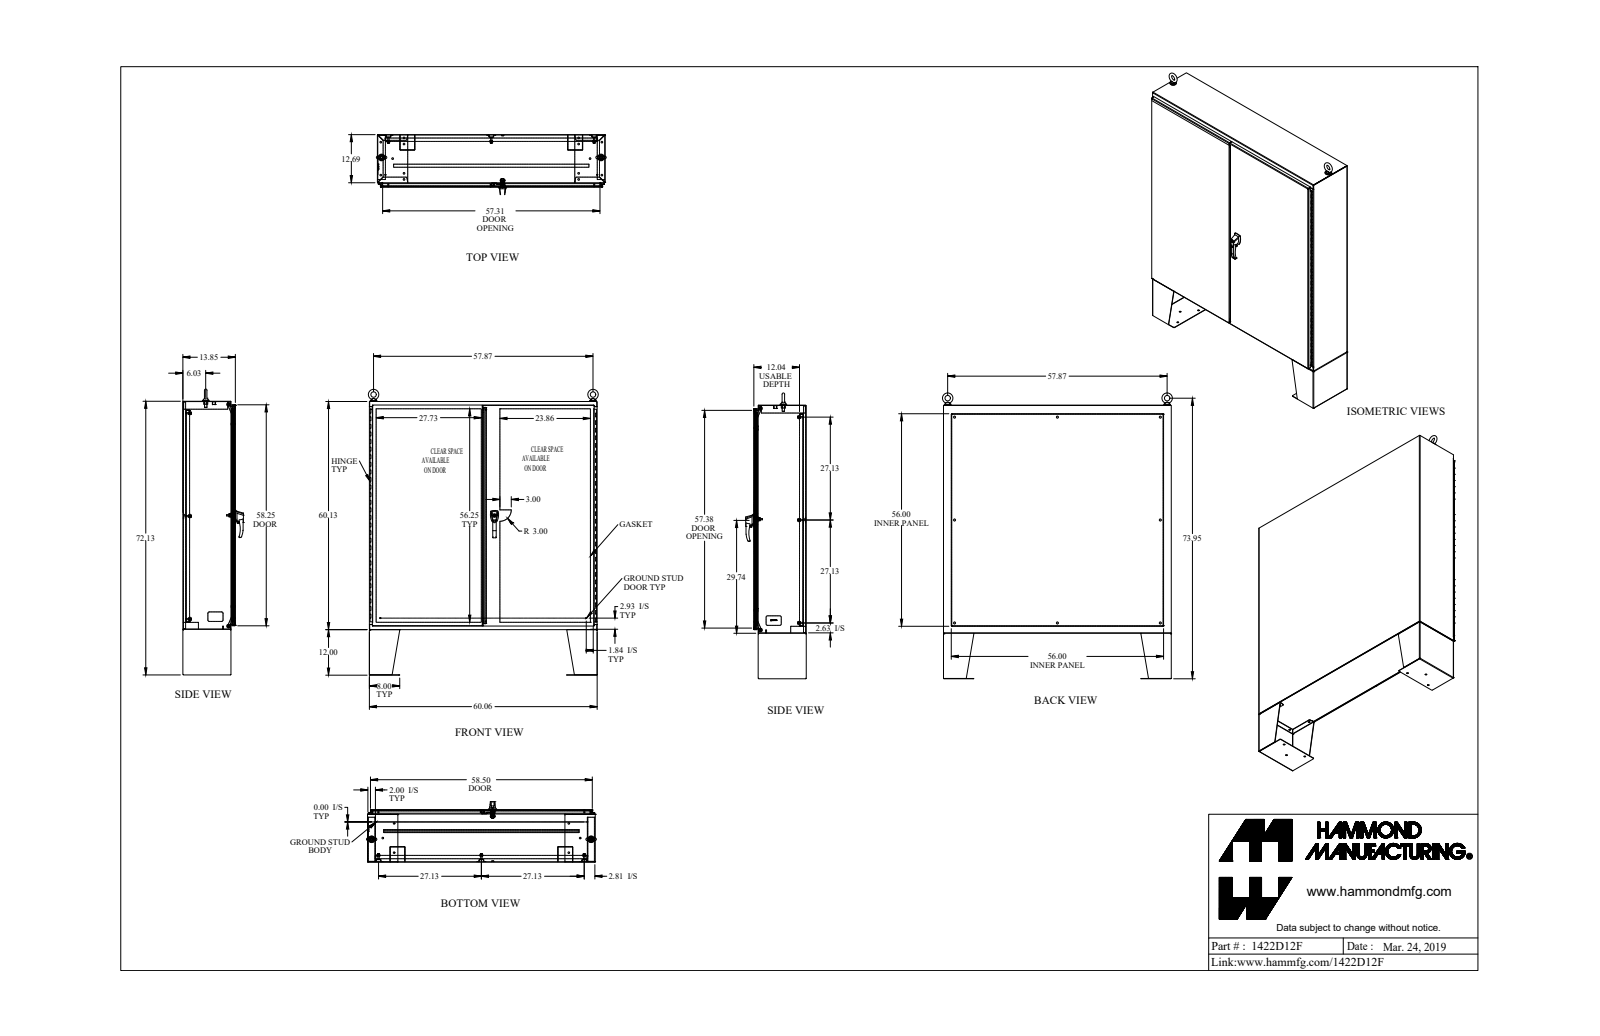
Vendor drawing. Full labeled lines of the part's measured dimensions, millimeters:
Part name (STEP PRODUCT): 1422D12F_Default
STEP written by: SolidWorks 2019 (CONFIG_CONTROL_DESIGN)
Units: millimetres
Bodies: 90 solids, 2769 faces (1280 planar, 1242 cylindrical, 247 other)
Overall size (bounding box): 1924.8 × 1552.5 × 405.5
Volume: 27 690 000 mm³ · Surface area: 21 600 000 mm²
Round holes (diameter × count): ⌀7.7 ×20, ⌀11.1 ×14, ⌀7.8 ×9, ⌀14.3 ×8, ⌀11.3 ×6, ⌀2.8 ×2, ⌀6.4 ×2, ⌀6.5 ×2, ⌀7.1 ×2, ⌀7.1 ×2, ⌀8 ×2, ⌀9.9 ×2
Round bosses / shafts (diameter × count): ⌀25.4 ×10, ⌀16.5 ×8, ⌀9.5 ×8, ⌀8.4 ×8, ⌀7.1 ×6, ⌀6.4 ×4, ⌀44.5 ×2, ⌀38.1 ×2
Partial cylindrical surfaces — rounded edges, fillets, slot ends (radius × count): R1.2 ×32, R3.6 ×32, R3.2 ×22, R0.5 ×16, R1.5 ×14, R2.9 ×12, R1.3 ×8, R4.7 ×8
Main face-to-face distances: 2.4, 2.4, 346.9, 349.3, 349.3, 351.7, 3.2, 306.5, 304.1, 42.8
Hole centre spacings: 152.4, 1491, 304.8, 1514.2, 457.2, 1552, 609.6, 1603.6
